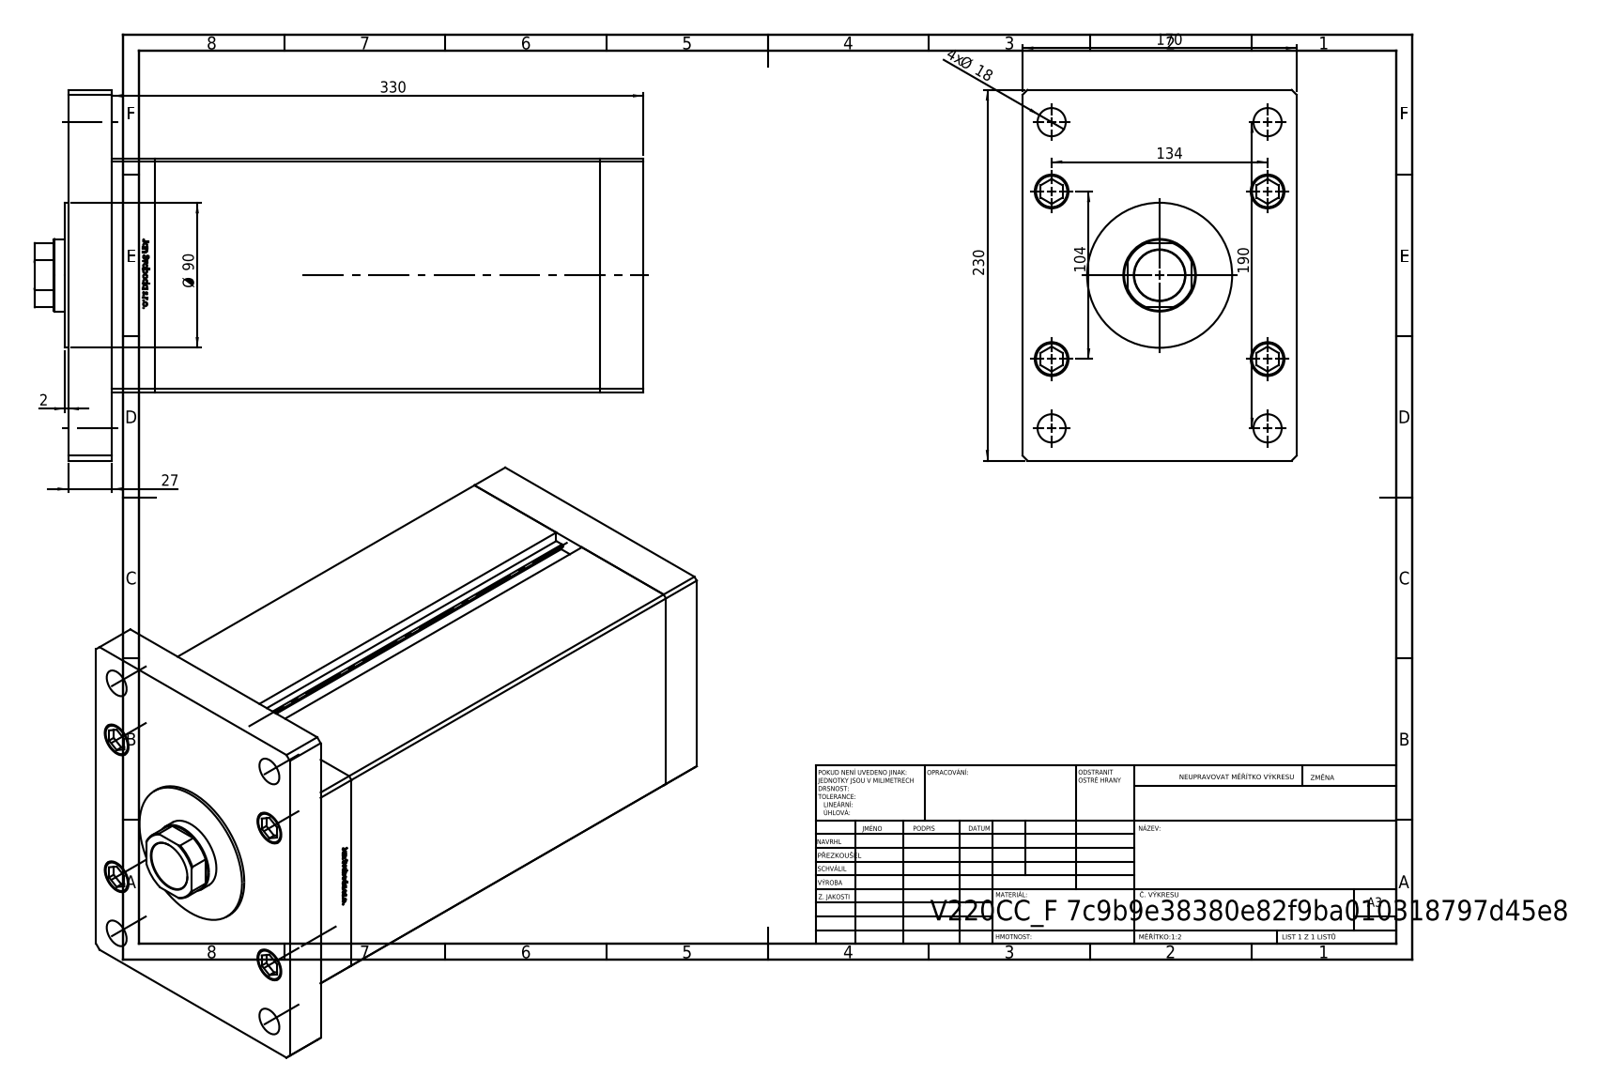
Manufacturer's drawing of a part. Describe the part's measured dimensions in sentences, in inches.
The part is named "ALLEN BOLT; V220C_F_MIDDLE; V220C_FRONT_F; V220C_VC_F (+2 more)". Its 3-D file was written by "SolidWorks 2019 (CONFIG_CONTROL_DESIGN)". It is 19 solids with 1310 faces: 517 planar, 187 cylindrical and 606 other. Overall it measures 14.882 by 9.055 by 6.693 inches. Its volume is 469 cubic inches and its surface area 1 066 square inches. Round holes: 9 of diameter 0.689, 5 of diameter 0.866, 4 of diameter 0.63, 4 of diameter 0.827, 2 of diameter 0.079, 2 of diameter 0.518, 1 of diameter 1.24, 1 of diameter 1.772, 1 of diameter 1.831. Round bosses or shafts: 9 of diameter 0.315, 5 of diameter 0.827, 1 of diameter 3.937, 1 of diameter 3.543. Partial cylindrical surfaces (rounded edges, fillets, slot ends): 2 of radius 0.037, 1 of radius 0.866. The main face-to-face distances are 1.063, 6.693, 11.929, 12.992, 5.709, 10.866, 2.126, 1.496, 14.055, 0.433. The hole center spacings are 2.402, 1.693, 3.339, 4.577, 5.276, 5.541, 5.787, 7.831.
